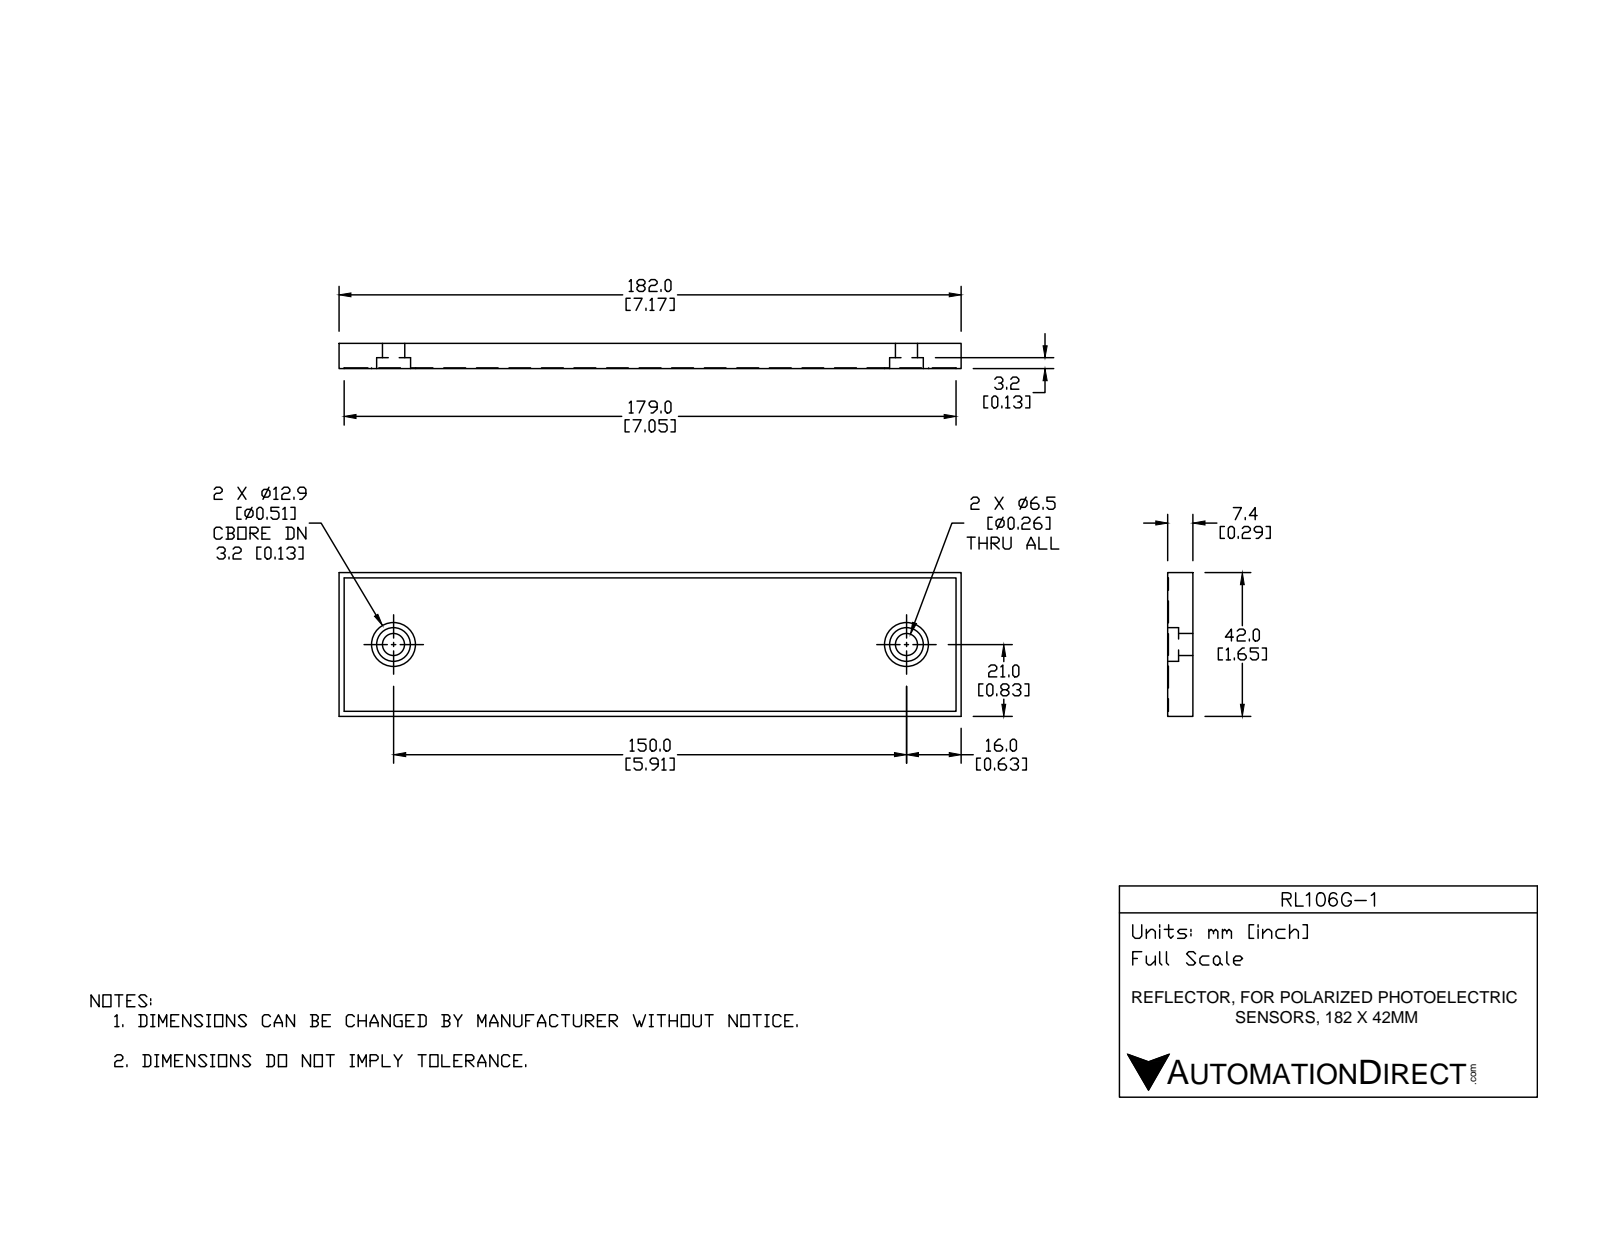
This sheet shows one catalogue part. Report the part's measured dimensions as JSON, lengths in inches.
{"part_name": "RL-106G-1", "step_written_by": "SolidWorks 2017 (AUTOMOTIVE_DESIGN)", "units": "inches", "bodies": {"solids": 1, "faces": 27, "planar": 15, "cylindrical": 12, "other": 0}, "overall_size": [7.165, 1.654, 0.291], "volume_in3": 3.323, "surface_area_in2": 29.36, "round_holes": [[0.256, 2], [0.39, 2]], "round_bosses_or_shafts": [[0.508, 2]], "face_to_face_distances": [0.283, 1.654, 0.291, 7.165, 0.165, 0.118, 0.126, 0.059, 1.594, 1.535], "hole_center_spacings": [5.906]}
